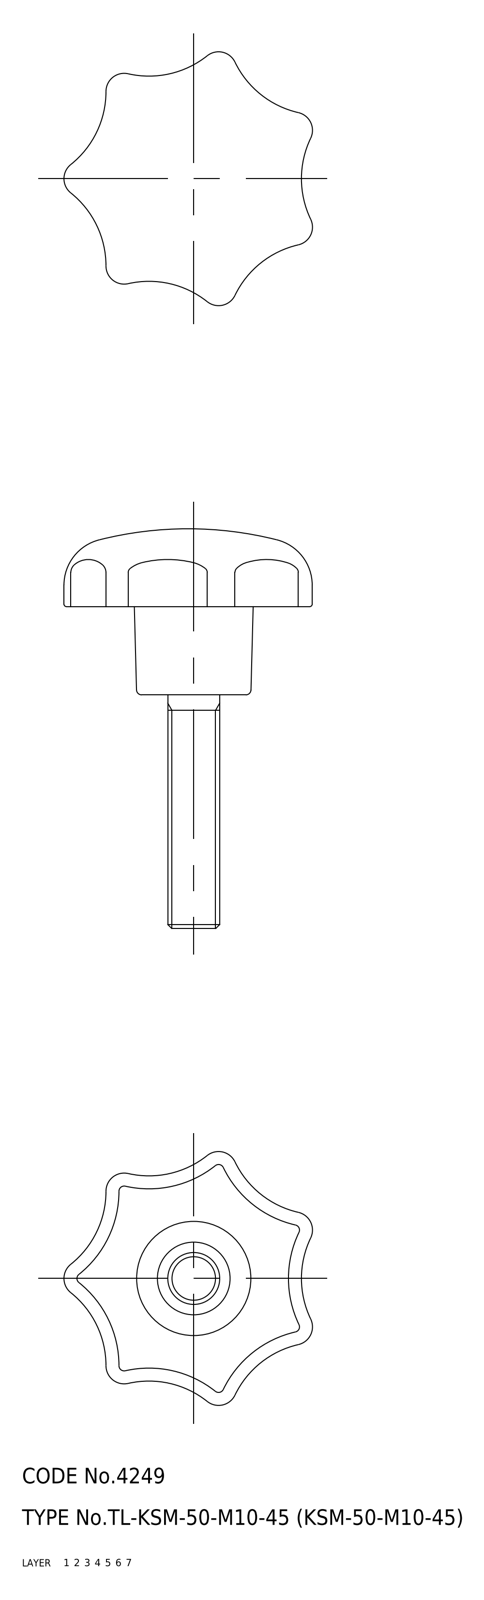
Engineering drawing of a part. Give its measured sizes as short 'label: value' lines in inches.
name: 67117584; 67117597
written by: CADfix (AUTOMOTIVE_DESIGN)
unit: in
bodies: 2 solids, 89 faces (0 planar, 0 cylindrical, 89 other)
size: 3.031 × 1.926 × 1.885
volume: 1.384 in³; area: 17.01 in²
